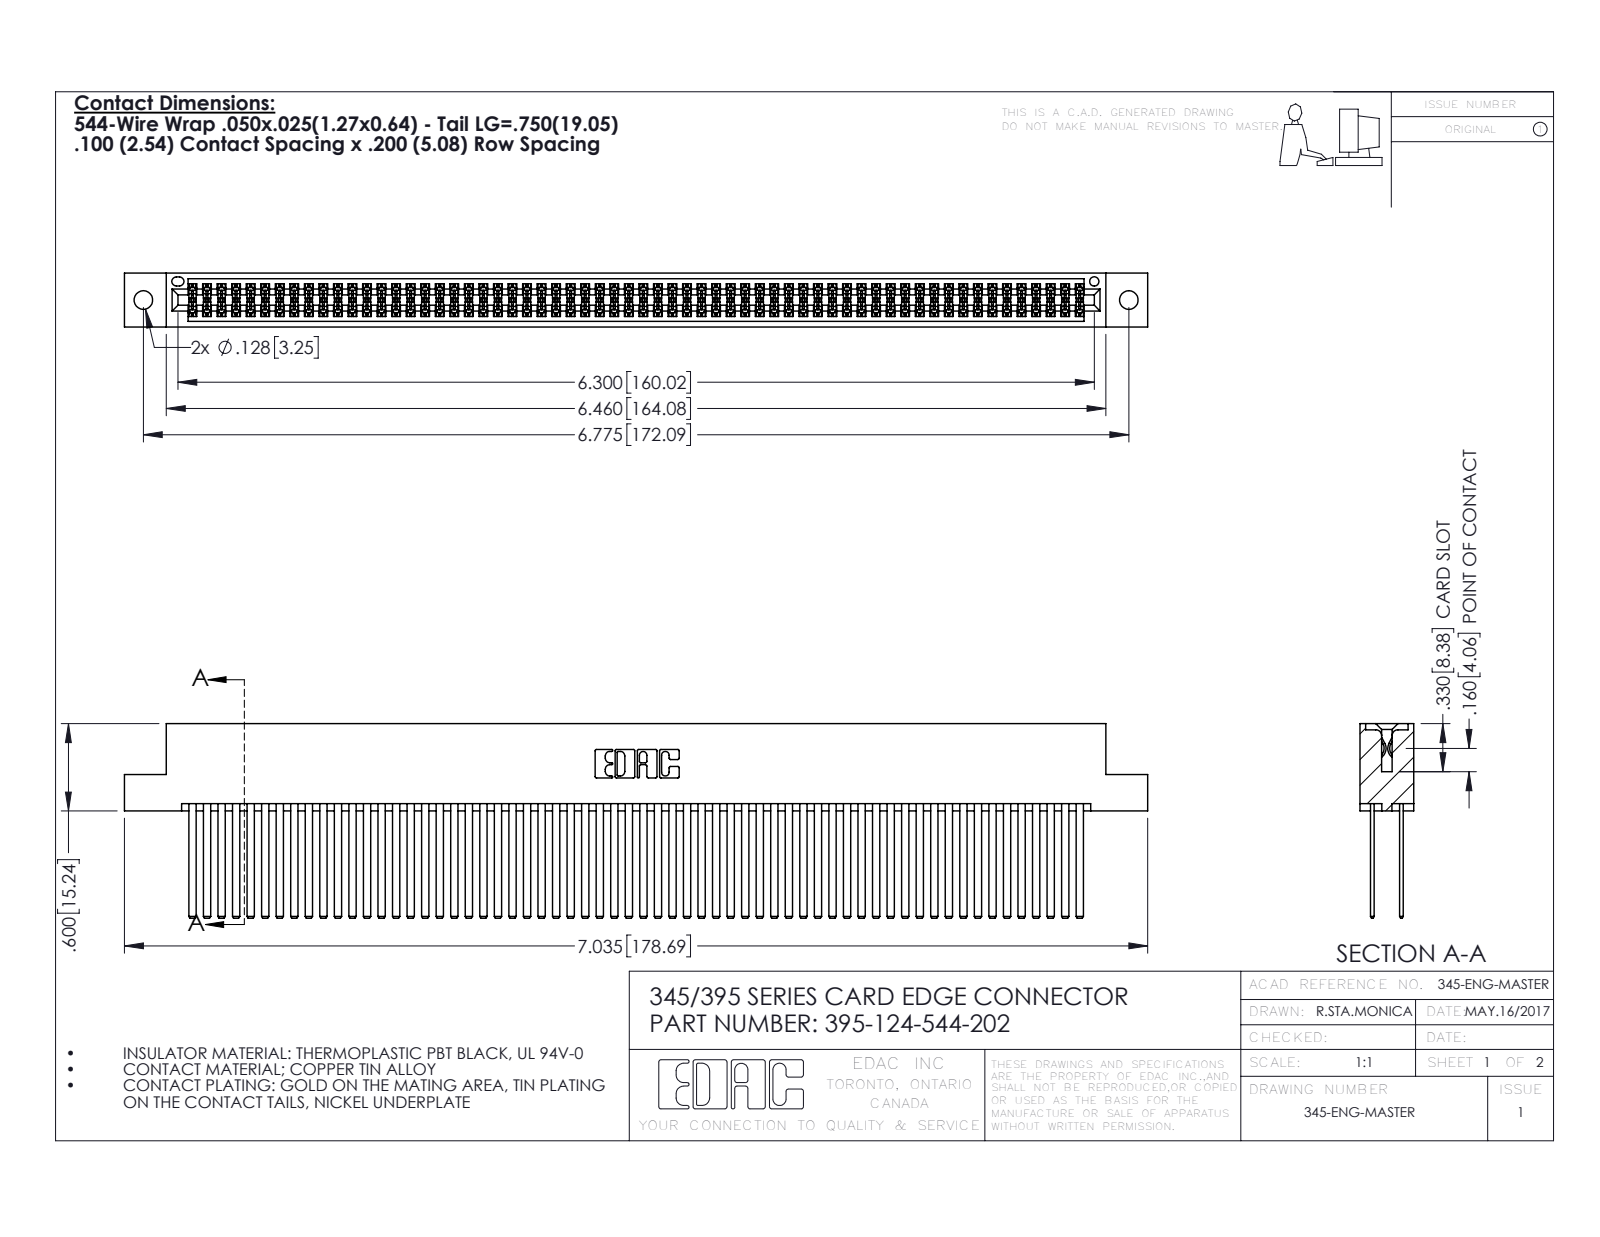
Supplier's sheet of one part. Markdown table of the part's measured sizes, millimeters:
| quantity | value |
| --- | --- |
| part name | 345 Part_Flush Mounting Lugs - 0.128 Dia; 395-124-544-202; 345-292-001_345-293-144 |
| STEP written by | SolidWorks 2016 (CONFIG_CONTROL_DESIGN) |
| units | millimeters |
| bodies | 125 solids, 5582 faces (3676 planar, 1906 cylindrical, 0 other) |
| overall size | 178.7 × 34 × 9.4 |
| volume | 19 240 mm³ |
| surface area | 33 660 mm² |
| round holes (diameter × count) | 3.3 × 2, 1.6 × 1 |
| partial cylindrical surfaces (radius × count) | 0.2 × 186, 0.3 × 22, 0.2 × 6, 0.8 × 6, 0.7 × 3, 0.4 × 2, 0.5 × 2, 0.6 × 2 |
| main face-to-face distances | 5.1, 0.6, 7.6, 1.8, 2.5, 6.9, 5.7, 4.4, 9.4, 1.3 |
| hole center spacings | 6.9, 166.1, 172.1 |
